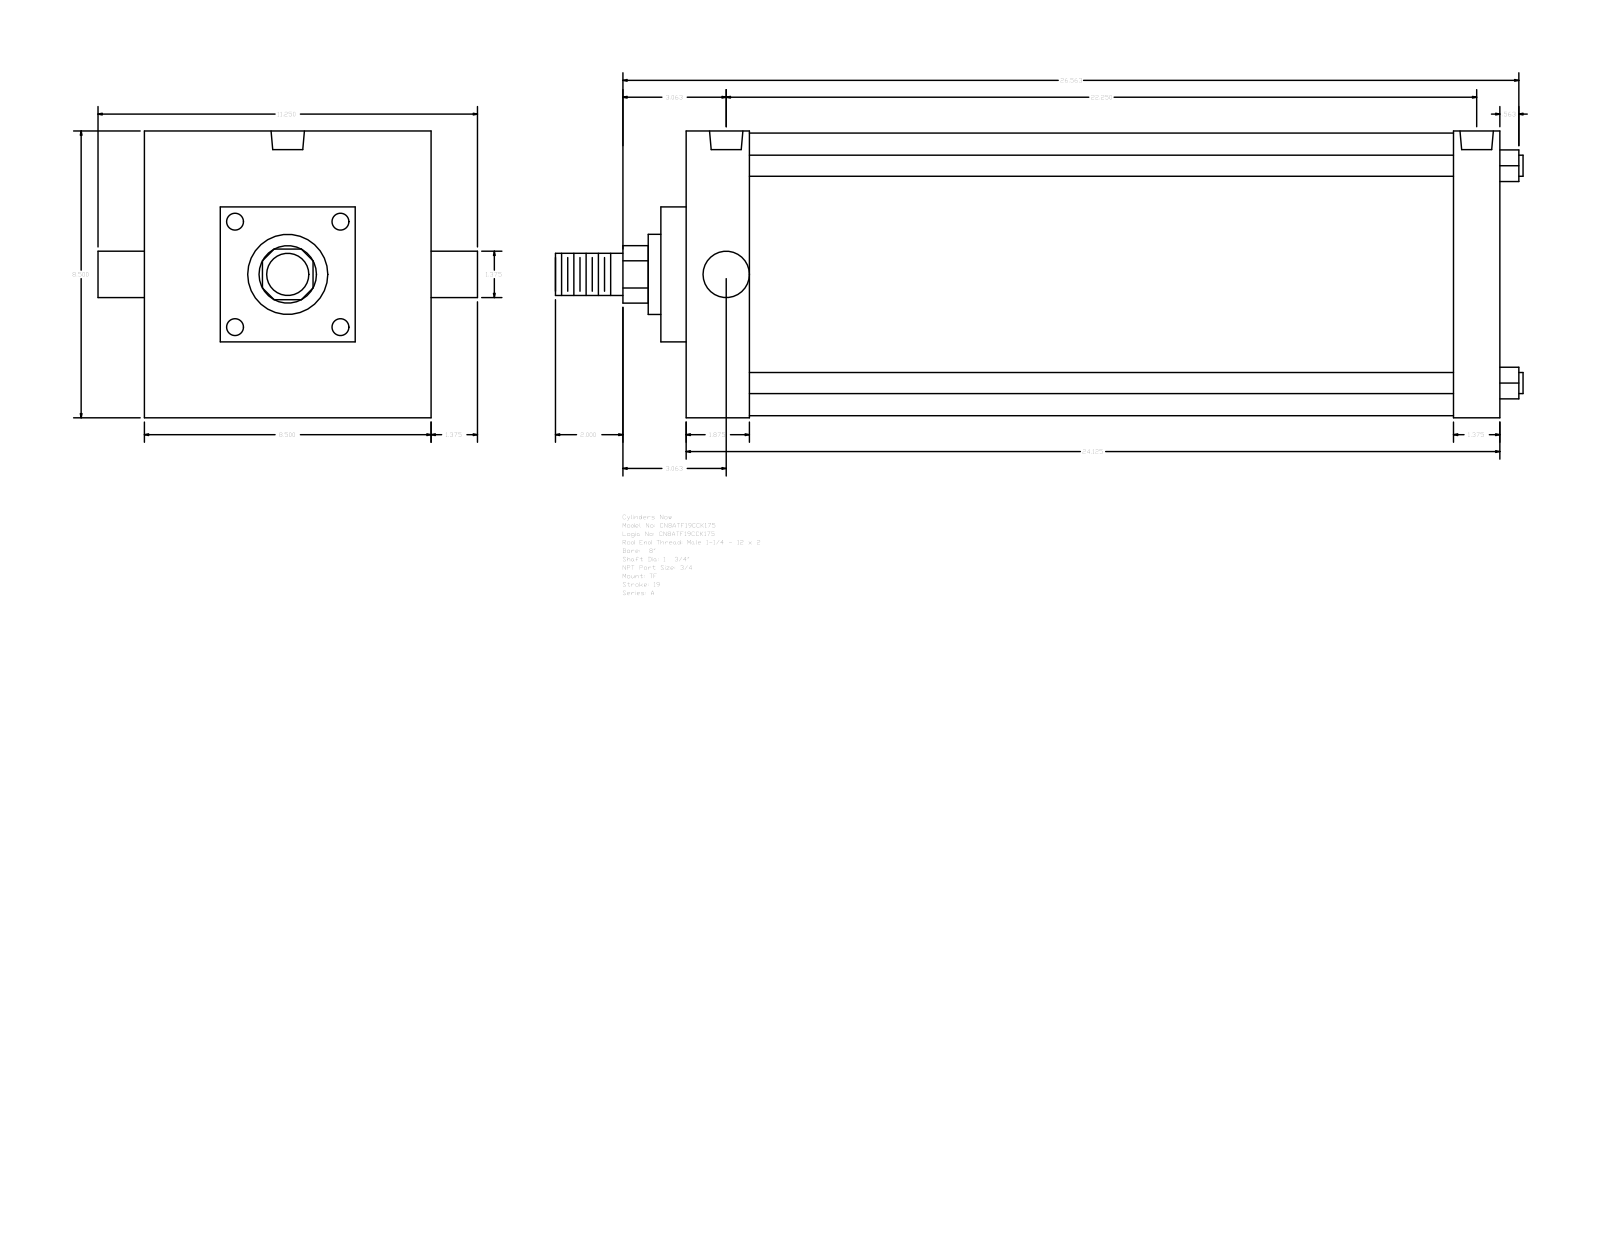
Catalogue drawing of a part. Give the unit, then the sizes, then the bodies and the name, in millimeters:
Units: millimetres
Overall size (bounding box): 728.66 × 285.75 × 215.9
Round holes (diameter × count): ⌀15.08 ×3, ⌀25.12 ×2
Round bosses / shafts (diameter × count): ⌀15.88 ×4, ⌀212.72 ×1, ⌀60.33 ×1, ⌀44.45 ×1, ⌀34.92 ×1, ⌀31.75 ×1
Partial cylindrical surfaces — rounded edges, fillets, slot ends (radius × count): R21.63 ×1
Main face-to-face distances: 612.78, 215.9, 47.63, 565.15, 577.86, 530.23, 34.92, 19.05, 57.15, 158.75
Hole centre spacings: 6.35, 558.8, 552.45, 565.15
Bodies: 0 solids, 89 faces (65 planar, 24 cylindrical, 0 other)
Part name (STEP PRODUCT): A_TF__0800_1.75
STEP written by: GSSL Pune (CONFIG_CONTROL_DESIGN)
